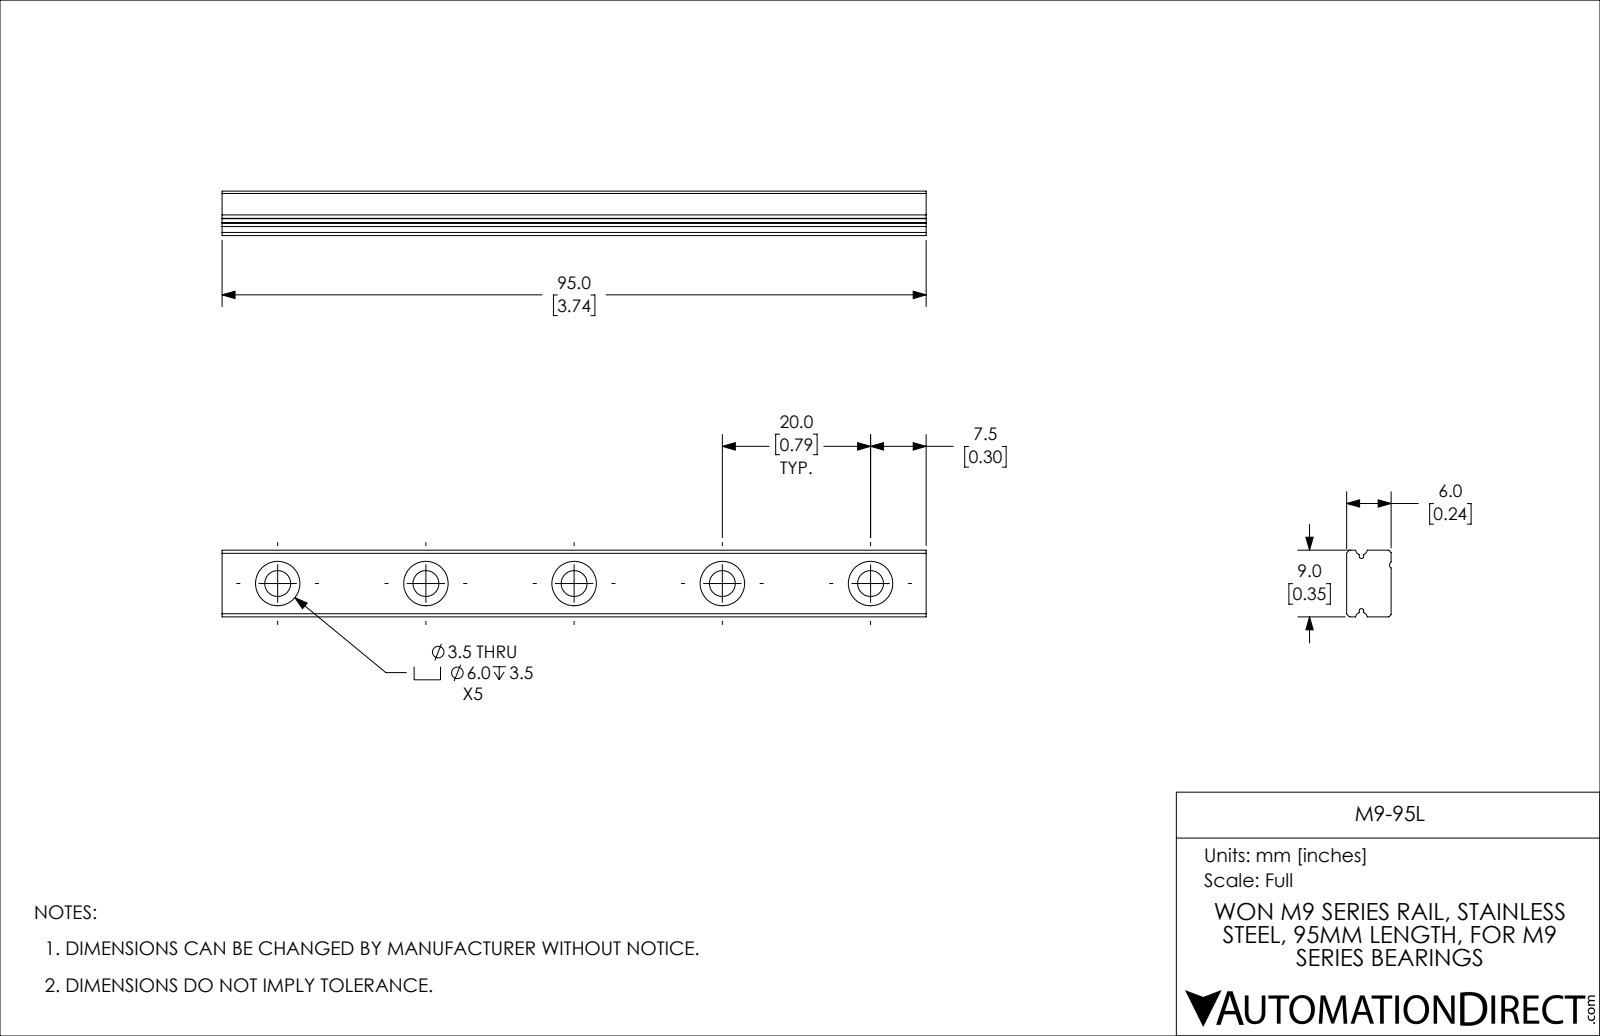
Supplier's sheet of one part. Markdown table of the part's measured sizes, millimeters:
| quantity | value |
| --- | --- |
| part name | M9-95L |
| STEP written by | SolidWorks 2019 (CONFIG_CONTROL_DESIGN) |
| units | millimeters |
| bodies | 1 solid, 50 faces (18 planar, 32 cylindrical, 0 other) |
| overall size | 95 × 9 × 6 |
| volume | 4 288 mm³ |
| surface area | 3 523 mm² |
| round holes (diameter × count) | 3.5 × 5, 6 × 5 |
| partial cylindrical surfaces (radius × count) | 0.32 × 2, 0.8 × 2, 0.95 × 2, 1 × 2, 0.5 × 1 |
| main face-to-face distances | 6, 9, 2.5, 3.5, 0.41, 95 |
| hole center spacings | 20, 40, 60, 80 |
